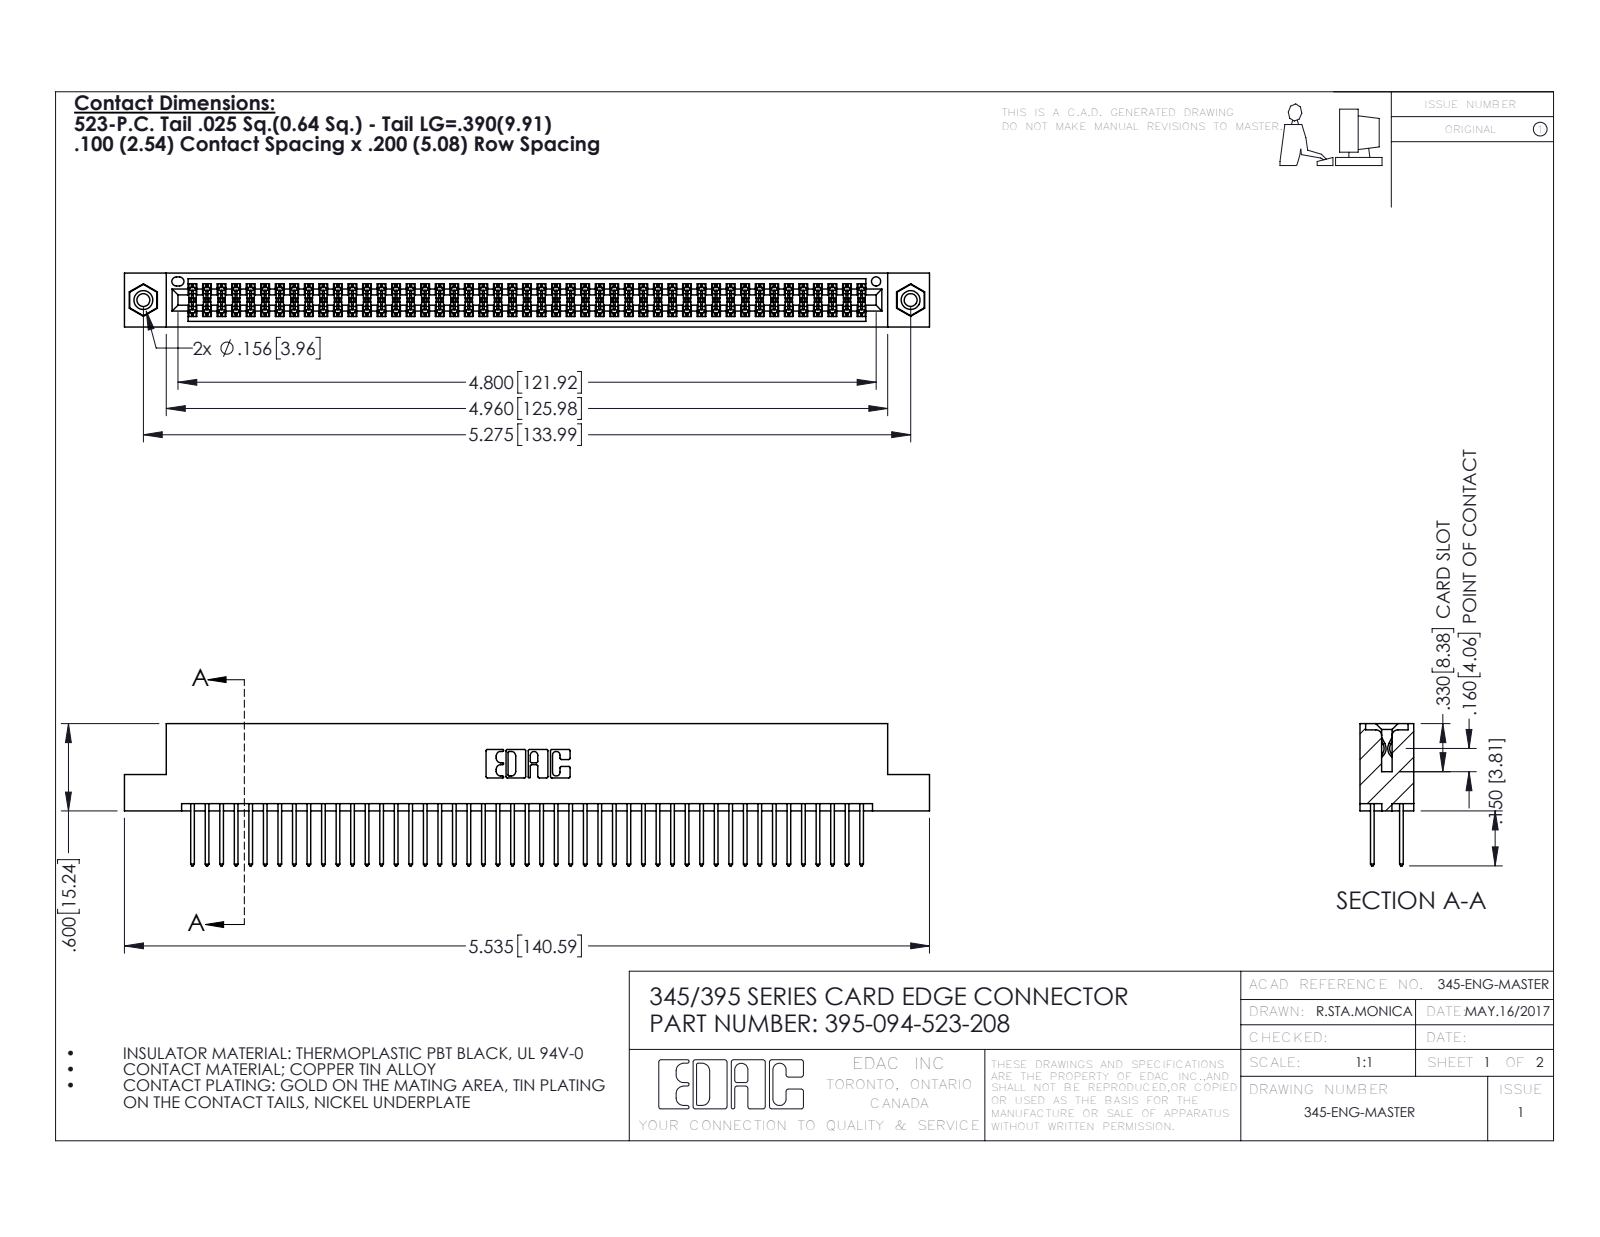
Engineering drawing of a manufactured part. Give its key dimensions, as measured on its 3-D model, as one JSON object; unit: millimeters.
{"part_name": "345-292-001_345-293-123; 395-094-523-208; 345 Part_Flush Mounting Lugs - 0.156 Dia-TI; 345-250-001_345-250-003-102", "step_written_by": "SolidWorks 2016 (CONFIG_CONTROL_DESIGN)", "units": "millimeters", "bodies": {"solids": 97, "faces": 4886, "planar": 3214, "cylindrical": 1656, "other": 16}, "overall_size": [140.6, 24.8, 9.4], "volume_mm3": 13900, "surface_area_mm2": 21500, "round_holes": [[2.3, 2], [3.2, 2], [4, 2], [1.6, 1]], "round_bosses_or_shafts": [[3.9, 2]], "partial_cylinders_radius": [[0.2, 141], [0.3, 94], [0.3, 22], [0.2, 6], [0.8, 6], [0.7, 3], [0.4, 2], [0.5, 2]], "face_to_face_distances": [1.8, 7.6, 5.1, 2.5, 6.9, 0.6, 9.4, 5.7, 4.4, 3.8], "hole_center_spacings": [6.9, 128, 134]}
